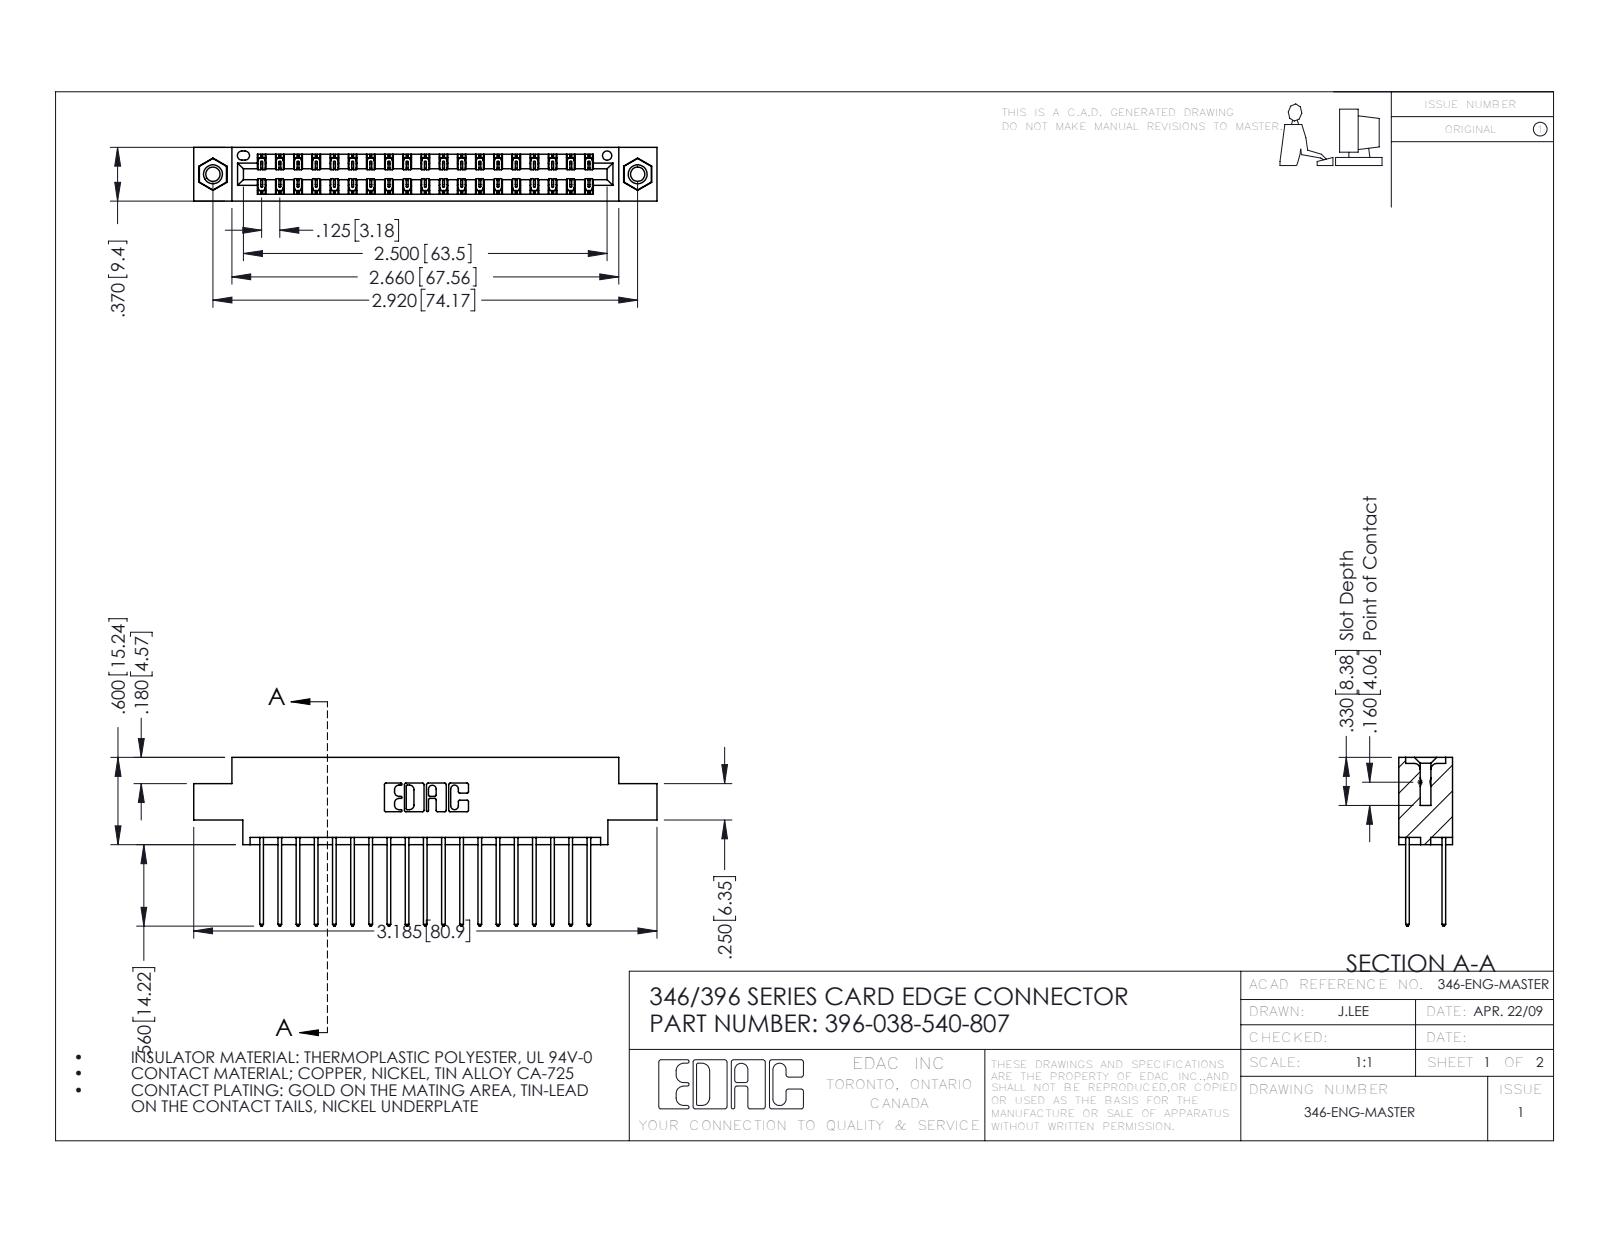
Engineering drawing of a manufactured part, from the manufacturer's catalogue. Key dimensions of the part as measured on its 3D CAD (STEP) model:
Part name (STEP PRODUCT): 345-292-001_345-293-140; 345-250-001_345-250-005-103; 346 Part_0.170 Offset - 0.156 Dia-TI; 396-038-540-807
STEP written by: SolidWorks 2016 (CONFIG_CONTROL_DESIGN)
Units: inches
Bodies: 41 solids, 2162 faces (1442 planar, 704 cylindrical, 16 other)
Overall size (bounding box): 3.185 × 1.16 × 0.37
Volume: 0.469 in³ · Surface area: 17.2 in²
Round holes (diameter × count): ⌀0.098 ×2, ⌀0.125 ×2, ⌀0.156 ×2, ⌀0.064 ×1
Round bosses / shafts (diameter × count): ⌀0.155 ×2
Partial cylindrical surfaces — rounded edges, fillets, slot ends (radius × count): R0.006 ×57, R0.01 ×38, R0.01 ×22, R0.007 ×6, R0.031 ×6, R0.026 ×3, R0.014 ×2, R0.022 ×2
Main face-to-face distances: 0.048, 0.322, 0.25, 0.37, 0.072, 0.298, 0.025, 0.275, 0.222, 0.148
Hole centre spacings: 0.246, 2.713, 2.92
